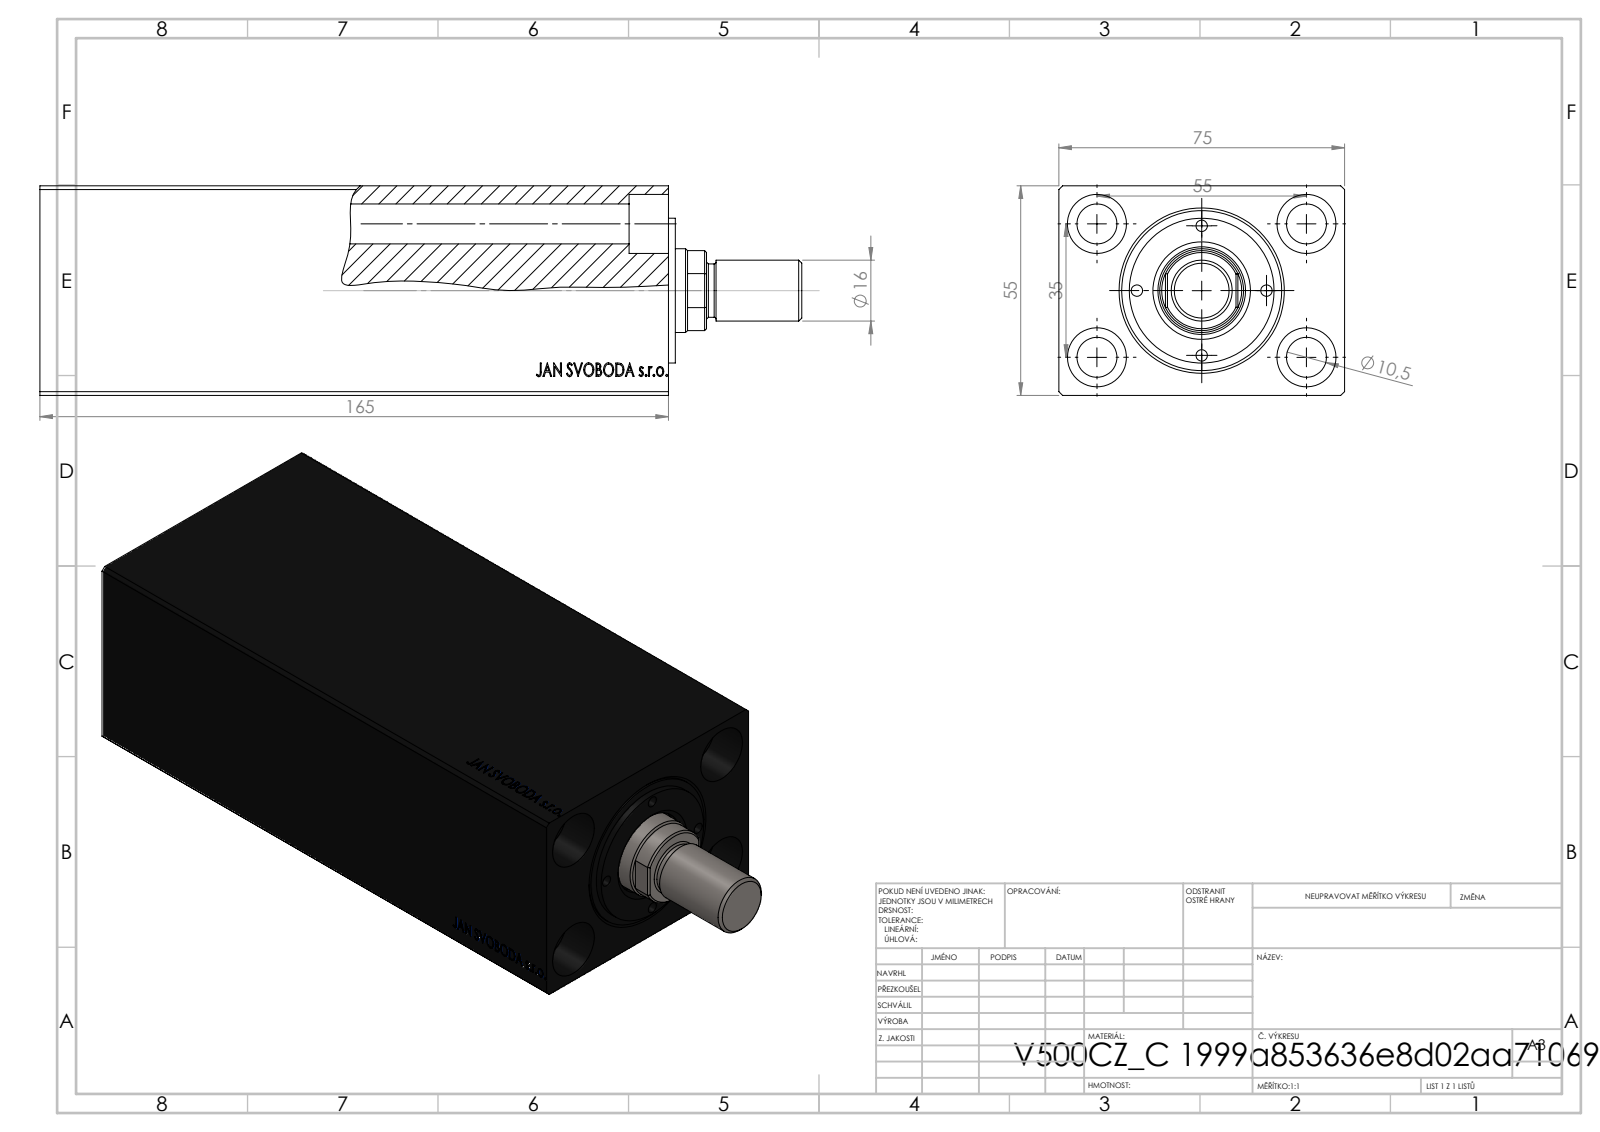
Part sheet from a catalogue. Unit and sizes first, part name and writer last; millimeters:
Units: millimetres
Overall size (bounding box): 165 × 75 × 55
Round holes (diameter × count): ⌀10.5 ×4, ⌀15.5 ×4, ⌀5.5 ×2, ⌀8 ×2, ⌀13.6 ×2, ⌀20 ×2, ⌀32 ×1, ⌀36 ×1, ⌀42 ×1
Main face-to-face distances: 55, 75, 165, 164.8, 10.33, 154.67, 151.2, 13.6, 13.8, 10
Hole centre spacings: 32.6, 35, 55, 65.19, 108, 128
Volume: 482 727 mm³ · Surface area: 90 135 mm²
Bodies: 1 solid, 824 faces (396 planar, 46 cylindrical, 382 other)
STEP written by: SolidWorks 2019 (CONFIG_CONTROL_DESIGN)
